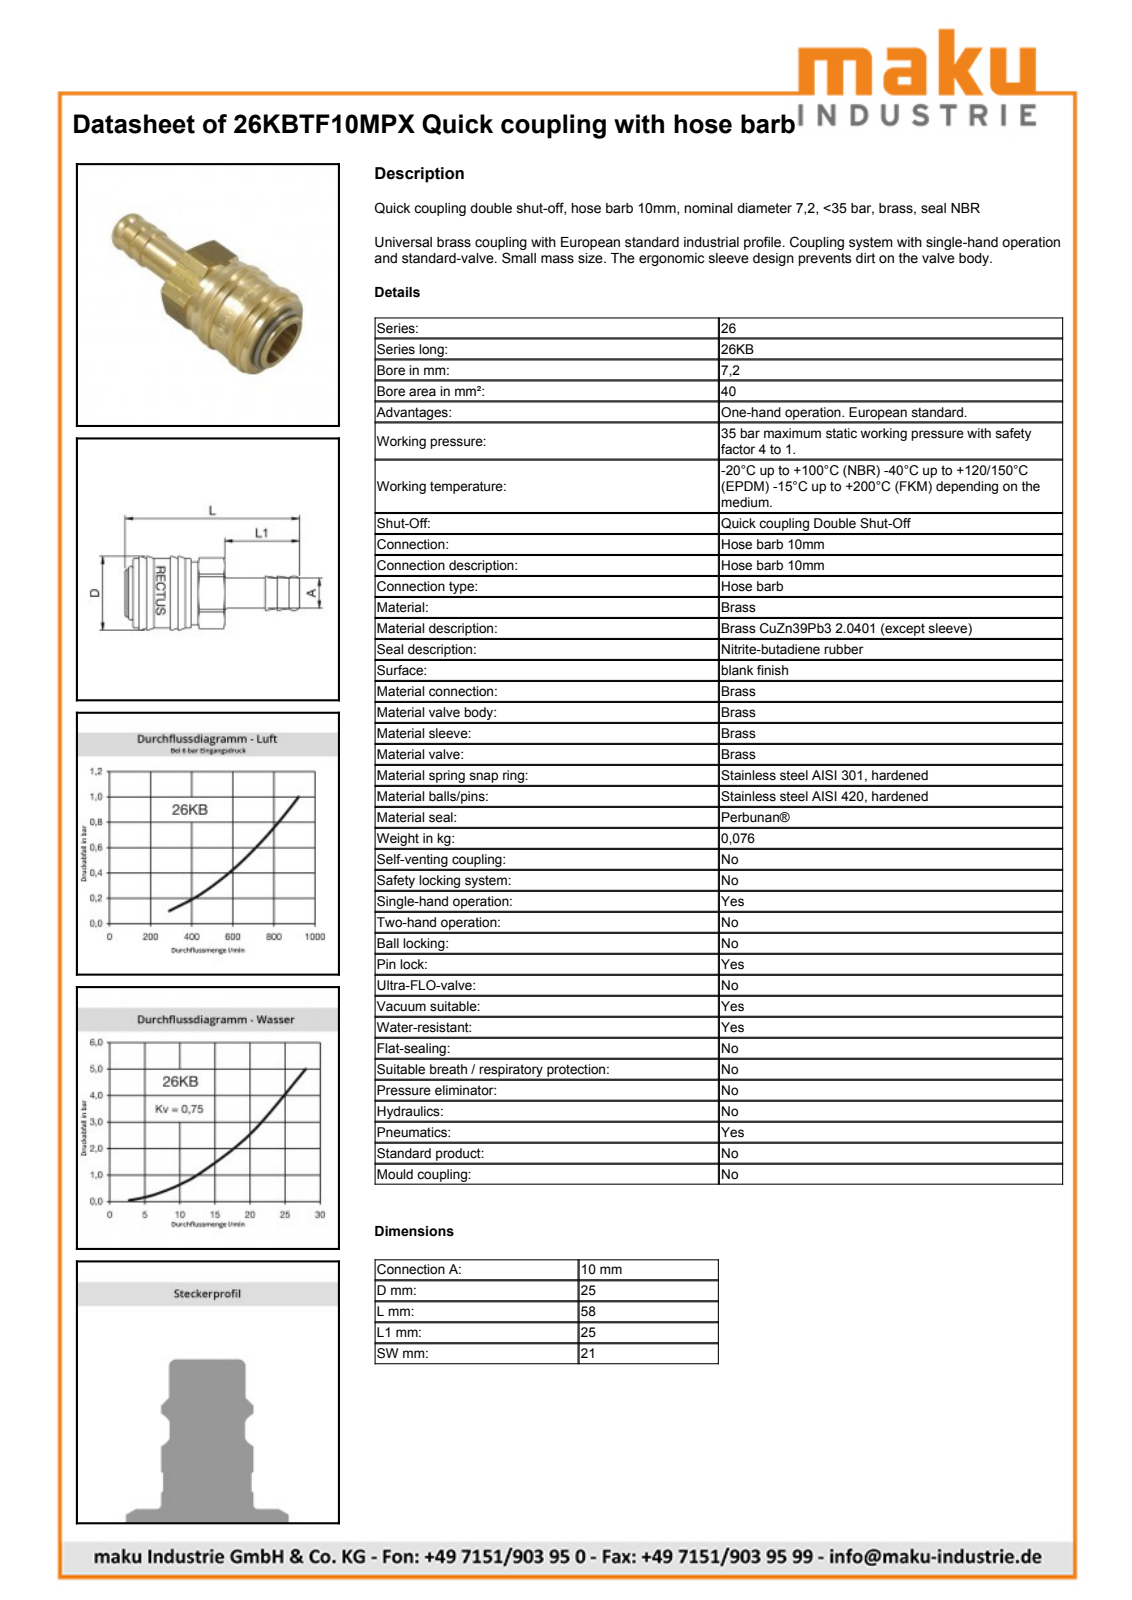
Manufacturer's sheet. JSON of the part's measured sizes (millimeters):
{"part_name": "D106706", "step_written_by": "Autodesk Inventor 2013 (AUTOMOTIVE_DESIGN)", "units": "millimeters", "bodies": {"solids": 2, "faces": 462, "planar": 175, "cylindrical": 59, "other": 228}, "overall_size": [58, 24.8, 24.8], "volume_mm3": 13408, "surface_area_mm2": 7432, "round_holes": [[16.1, 1], [17, 1], [21.1, 1]], "round_bosses_or_shafts": [[23.3, 1], [21, 1], [18, 1], [16.65, 1], [15.95, 1], [14.95, 1], [10.1, 1]], "partial_cylinders_radius": [[7.74, 1], [11.55, 1], [11.85, 1]], "face_to_face_distances": [21, 30.35, 2.65, 33, 20.98, 21.02, 18.35, 12, 58, 55.35]}
